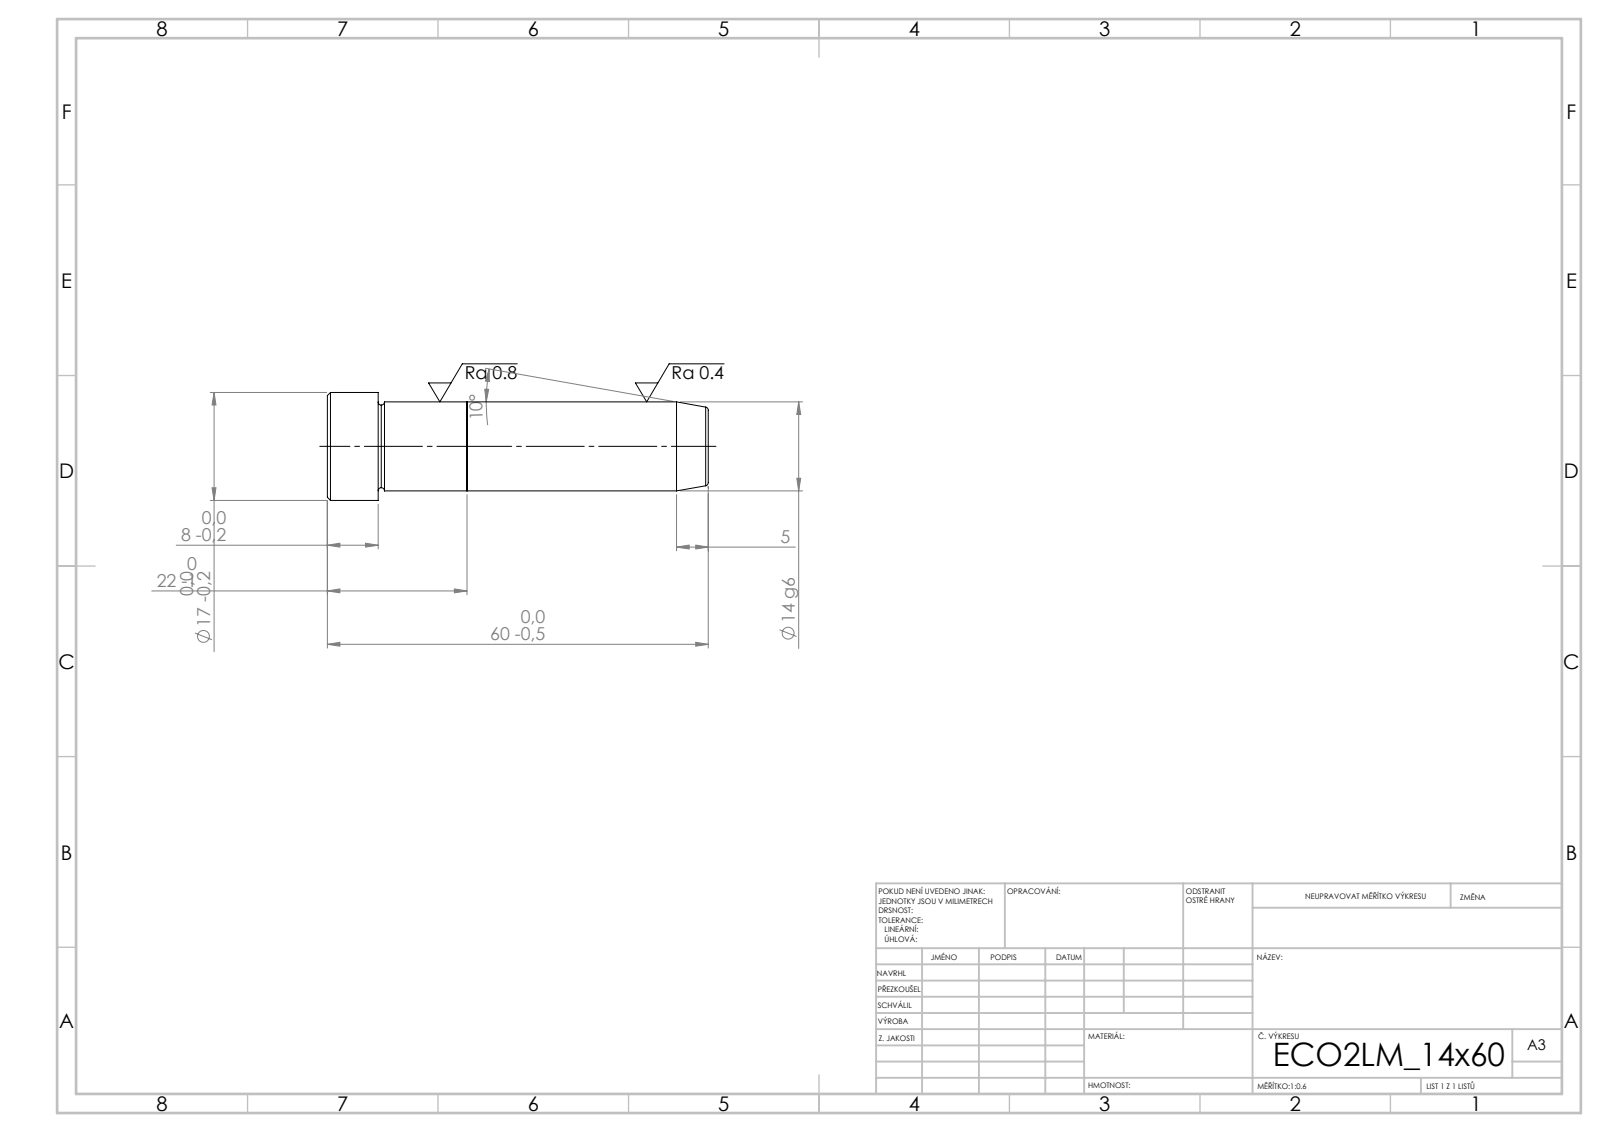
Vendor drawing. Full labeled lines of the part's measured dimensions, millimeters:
STEP written by: SolidWorks 2019 (CONFIG_CONTROL_DESIGN)
Units: millimetres
Bodies: 2 solids, 21 faces (5 planar, 6 cylindrical, 10 other)
Overall size (bounding box): 60 × 17 × 17
Volume: 9 703 mm³ · Surface area: 3 430 mm²
Round bosses / shafts (diameter × count): ⌀17 ×1, ⌀14 ×1
Main face-to-face distances: 22, 38, 60, 52, 14, 8
